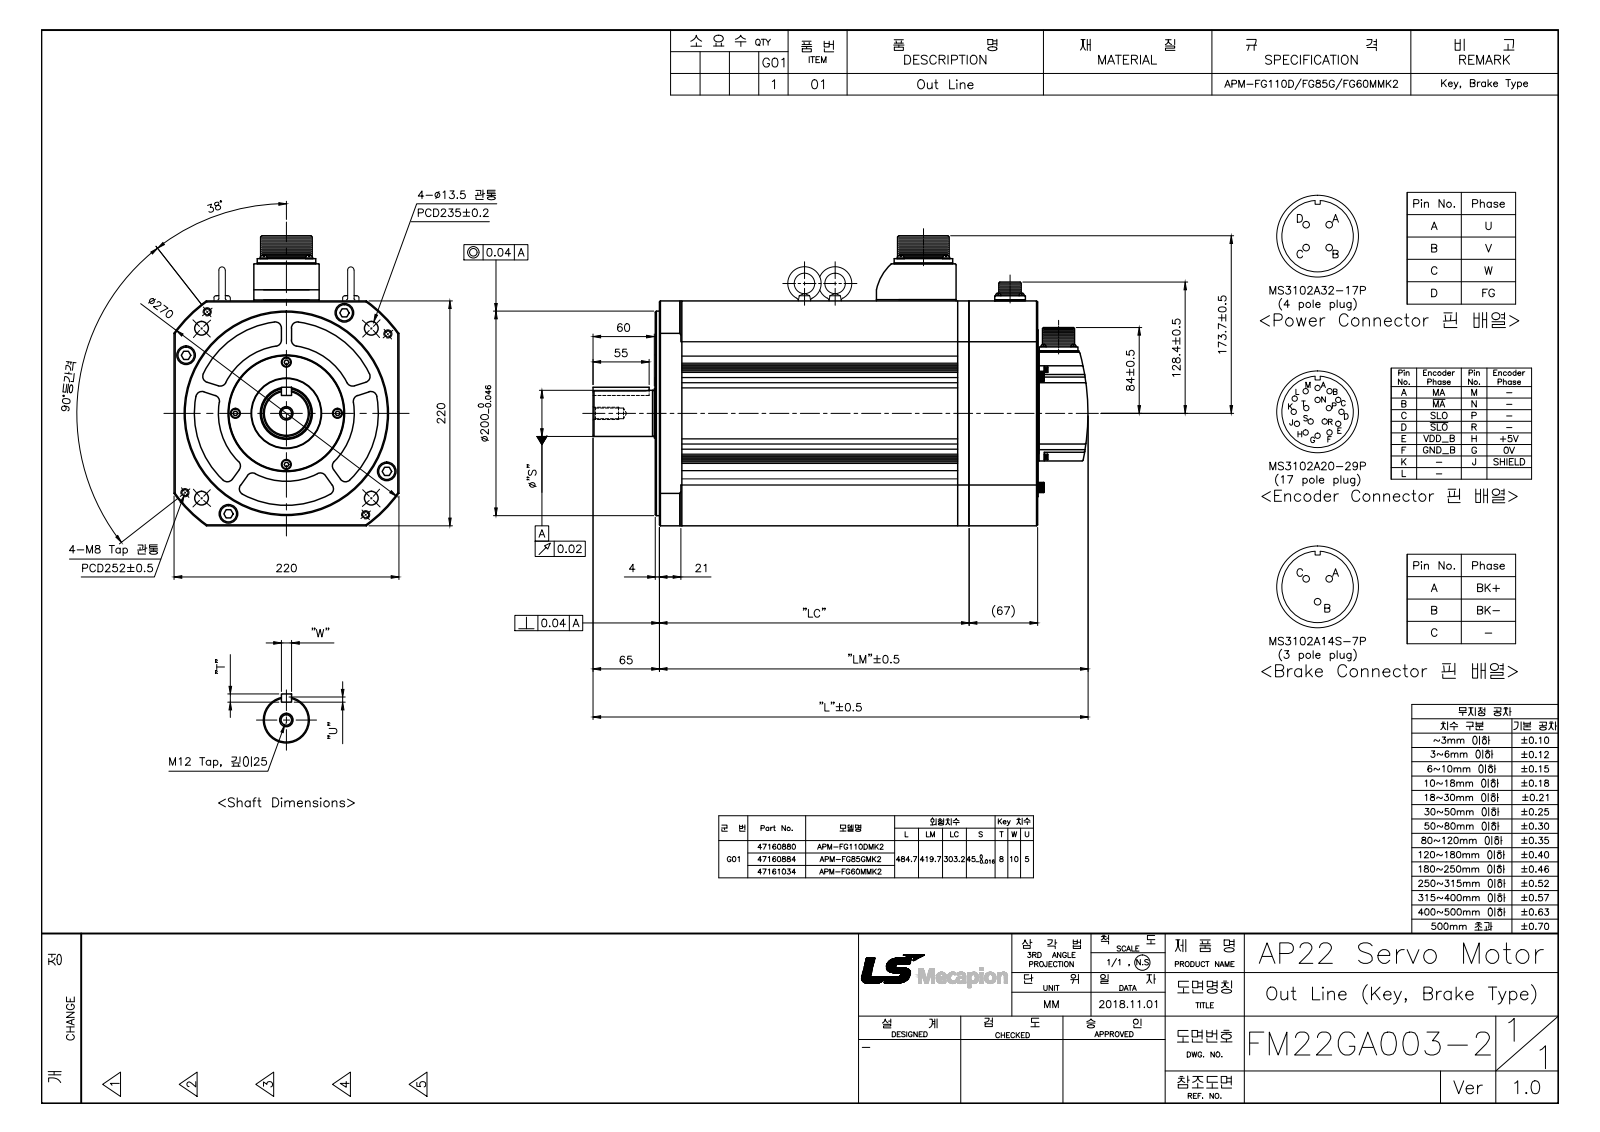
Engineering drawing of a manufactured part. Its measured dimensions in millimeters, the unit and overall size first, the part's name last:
Units: millimetres
Overall size (bounding box): 484.7 × 283.7 × 220
Round holes (diameter × count): ⌀2.5 ×12, ⌀3 ×12, ⌀3.05 ×10, ⌀8 ×8, ⌀6.8 ×7, ⌀12 ×7, ⌀18 ×5, ⌀3.3 ×4, ⌀3.5 ×4, ⌀3.6 ×4, ⌀3.7 ×4, ⌀4 ×4
Round bosses / shafts (diameter × count): ⌀1.6 ×20, ⌀5.4 ×8, ⌀6 ×7, ⌀16 ×4, ⌀8.5 ×4, ⌀7 ×4, ⌀5.5 ×4, ⌀10.2 ×3
Partial cylindrical surfaces — rounded edges, fillets, slot ends (radius × count): R1 ×122, R6 ×24, R2 ×17, R5 ×17, R4 ×14, R4.5 ×12, R0.5 ×8, R2.5 ×4
Main face-to-face distances: 11.2, 281.2, 270, 40, 220, 180, 140, 67, 21, 14
Hole centre spacings: 89.44, 156.9, 16.26, 17.11, 20.79, 23, 27.23, 29.4
Volume: 16 130 000 mm³ · Surface area: 985 791 mm²
Bodies: 74 solids, 2573 faces (901 planar, 1006 cylindrical, 666 other)
Part name (STEP PRODUCT): FM22GA003-2G05_Out Line(APM-FG110D_K2,FG85G_K2,FG60M_K2)
STEP written by: SolidWorks 2011 (AUTOMOTIVE_DESIGN)
